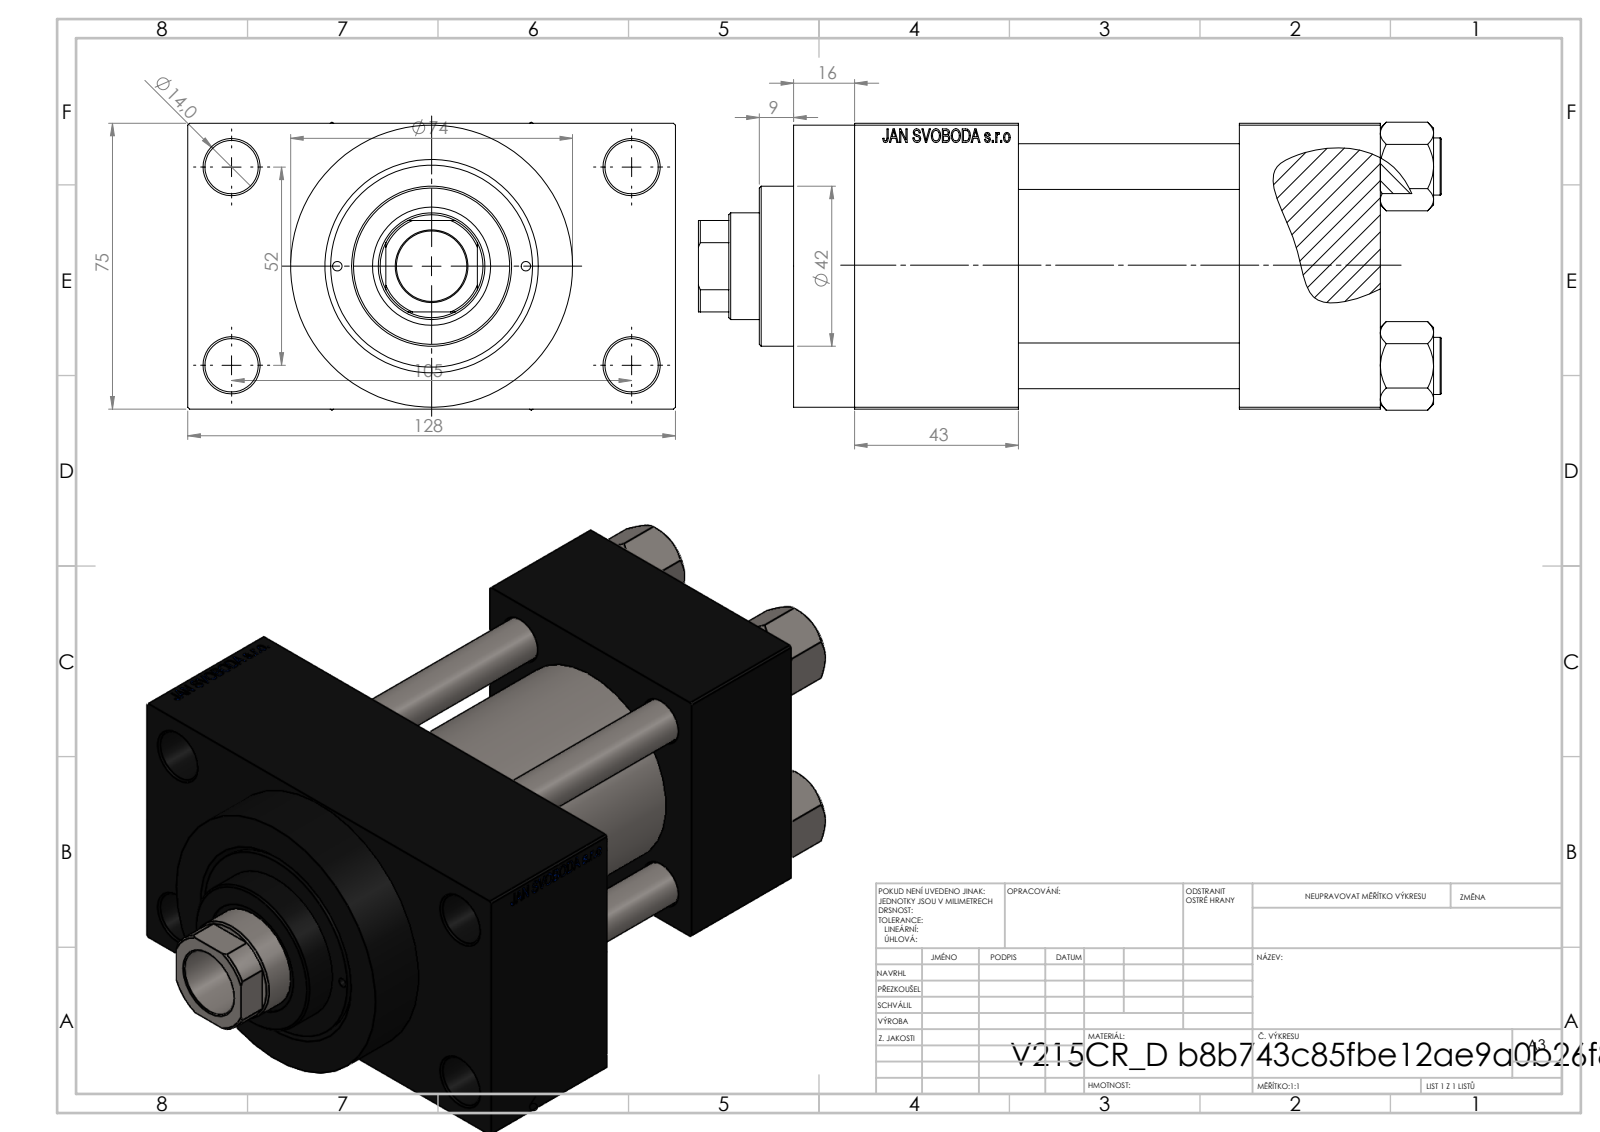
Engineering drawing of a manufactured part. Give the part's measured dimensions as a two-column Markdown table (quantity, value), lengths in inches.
| quantity | value |
| --- | --- |
| part name | V215CR_D_Body; V215_VC_A; V215CR_D_TYCINKA; NUT_M5_D (+1 more) |
| STEP written by | SolidWorks 2019 (CONFIG_CONTROL_DESIGN) |
| units | inches |
| bodies | 11 solids, 1111 faces (499 planar, 92 cylindrical, 520 other) |
| overall size | 7.677 × 5.039 × 2.974 |
| volume | 49.18 in³ |
| surface area | 264.3 in² |
| round holes (diameter × count) | 0.472 × 4, 0.551 × 4, 0.098 × 2, 0.276 × 2, 0.825 × 2, 1.181 × 2, 0.728 × 1, 1.102 × 1, 1.22 × 1, 1.614 × 1, 1.969 × 1, 2.087 × 1 |
| round bosses / shafts (diameter × count) | 0.591 × 4, 2.913 × 1, 2.205 × 1, 1.654 × 1 |
| partial cylindrical surfaces (radius × count) | 0.531 × 1 |
| main face-to-face distances | 2.953, 2.283, 1.457, 3.74, 1.043, 5.433, 3.976, 1.693, 3.996, 0.63 |
| hole center spacings | 1.031, 1.037, 1.456, 1.497, 2.059, 2.253, 2.3, 2.307 |
